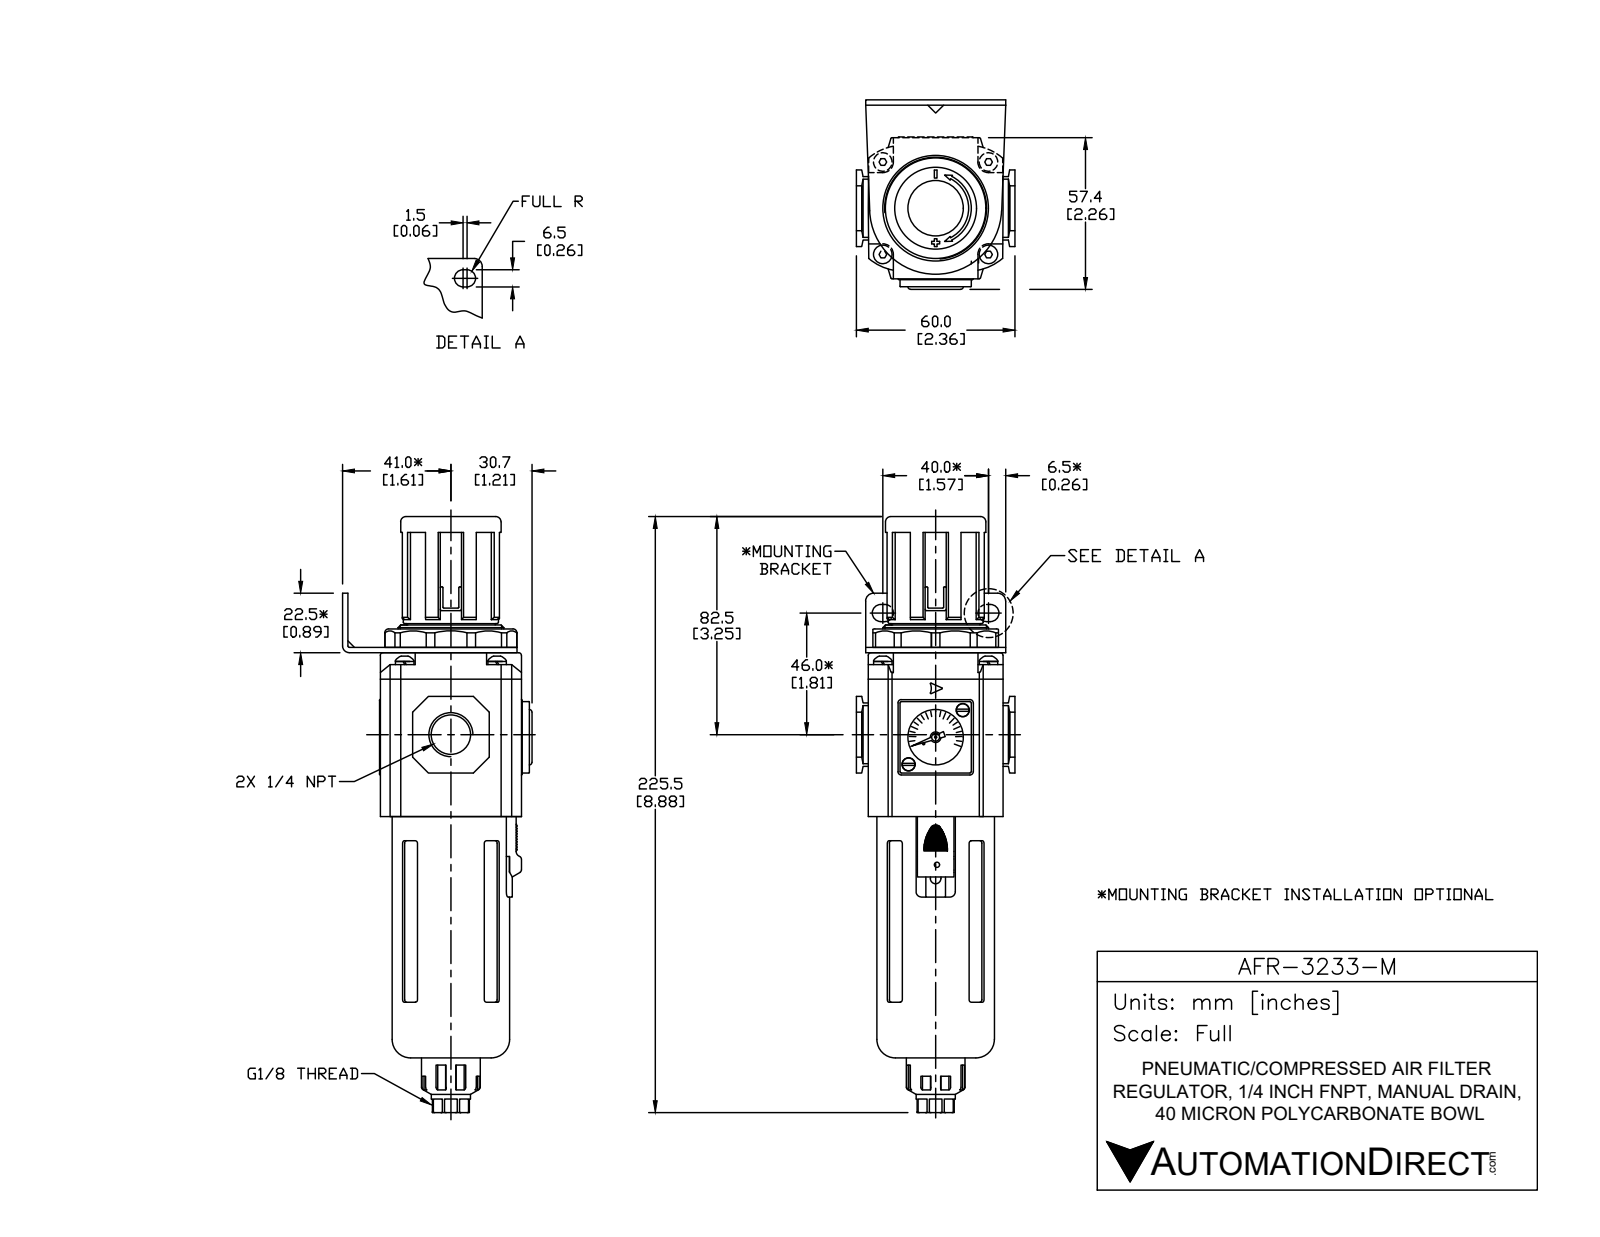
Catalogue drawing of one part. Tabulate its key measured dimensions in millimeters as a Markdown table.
| quantity | value |
| --- | --- |
| part name | AFR-3233-M |
| STEP written by | SolidWorks 2015 (CONFIG_CONTROL_DESIGN) |
| units | millimeters |
| bodies | 16 solids, 606 faces (370 planar, 172 cylindrical, 64 other) |
| overall size | 225.6 × 72 × 60 |
| volume | 276 308 mm³ |
| surface area | 69 828 mm² |
| round holes (diameter × count) | 3 × 6, 2 × 1, 6.2 × 1, 11.13 × 1, 16 × 1, 21 × 1, 30 × 1, 32 × 1, 35.2 × 1 |
| round bosses / shafts (diameter × count) | 5.5 × 4, 2.7 × 2, 44 × 1, 40 × 1, 38 × 1, 36 × 1, 33.5 × 1, 20.46 × 1 |
| partial cylindrical surfaces (radius × count) | 2.2 × 18, 1 × 12, 1.2 × 10, 0.5 × 8, 9.5 × 8, 3.25 × 6, 4 × 5, 0.3 × 4 |
| main face-to-face distances | 2, 62, 64, 53.4, 51, 39.6, 1, 55.5, 52.4, 4.5 |
| hole center spacings | 26.58, 14.5, 35, 40, 53.15, 28.99 |
